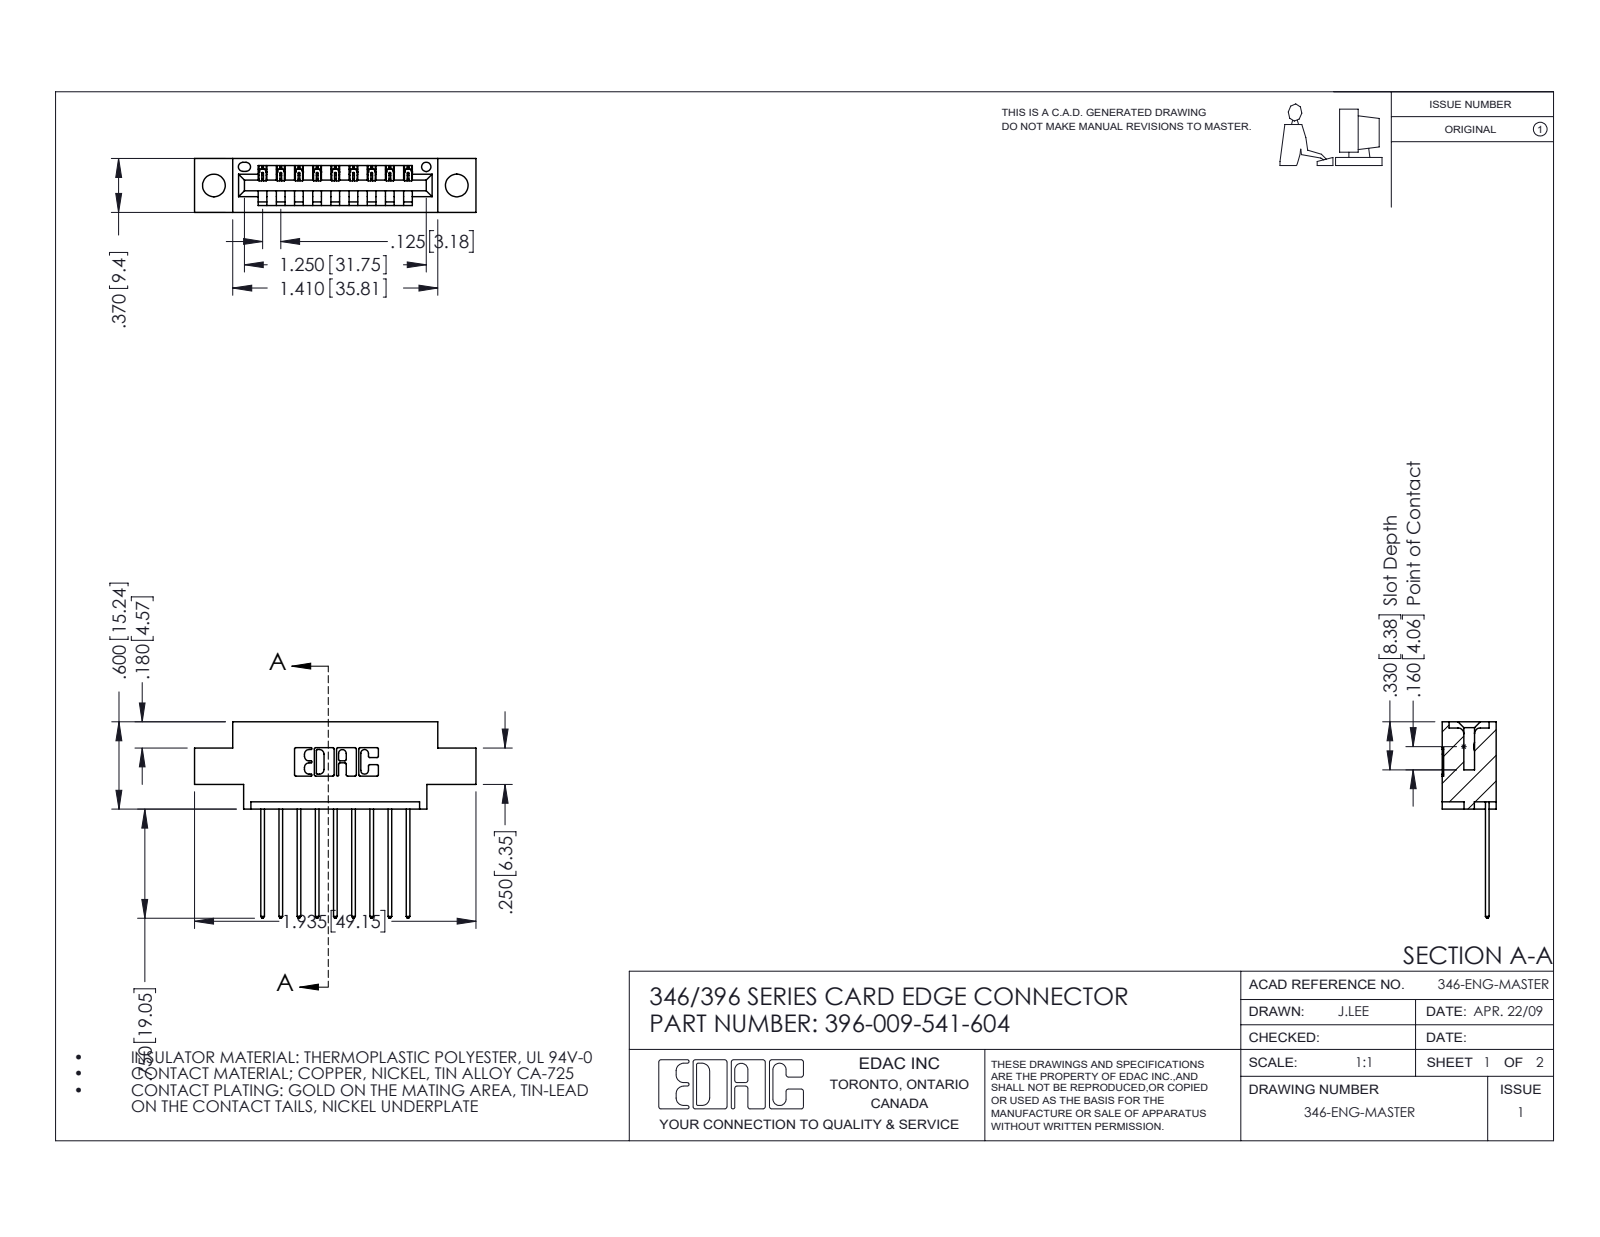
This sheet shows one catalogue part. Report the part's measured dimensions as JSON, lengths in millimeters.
{"part_name": "396-009-541-604; 345-292-001_345-293-141; 346 Part_0.170 Offset - 0.156 Dia-TH", "step_written_by": "SolidWorks 2016 (CONFIG_CONTROL_DESIGN)", "units": "millimeters", "bodies": {"solids": 10, "faces": 648, "planar": 440, "cylindrical": 208, "other": 0}, "overall_size": [49.1, 34.3, 9.4], "volume_mm3": 4260, "surface_area_mm2": 5117, "round_holes": [[4, 2], [1.6, 1]], "partial_cylinders_radius": [[0.3, 22], [0.2, 18], [0.3, 18], [0.2, 6], [0.8, 6], [0.7, 3], [0.8, 2], [1, 2]], "face_to_face_distances": [6.4, 9.4, 1.2, 8.2, 1.8, 7.6, 0.6, 3.8, 5.6, 2.5], "hole_center_spacings": [6.2, 37.2, 42.4]}
